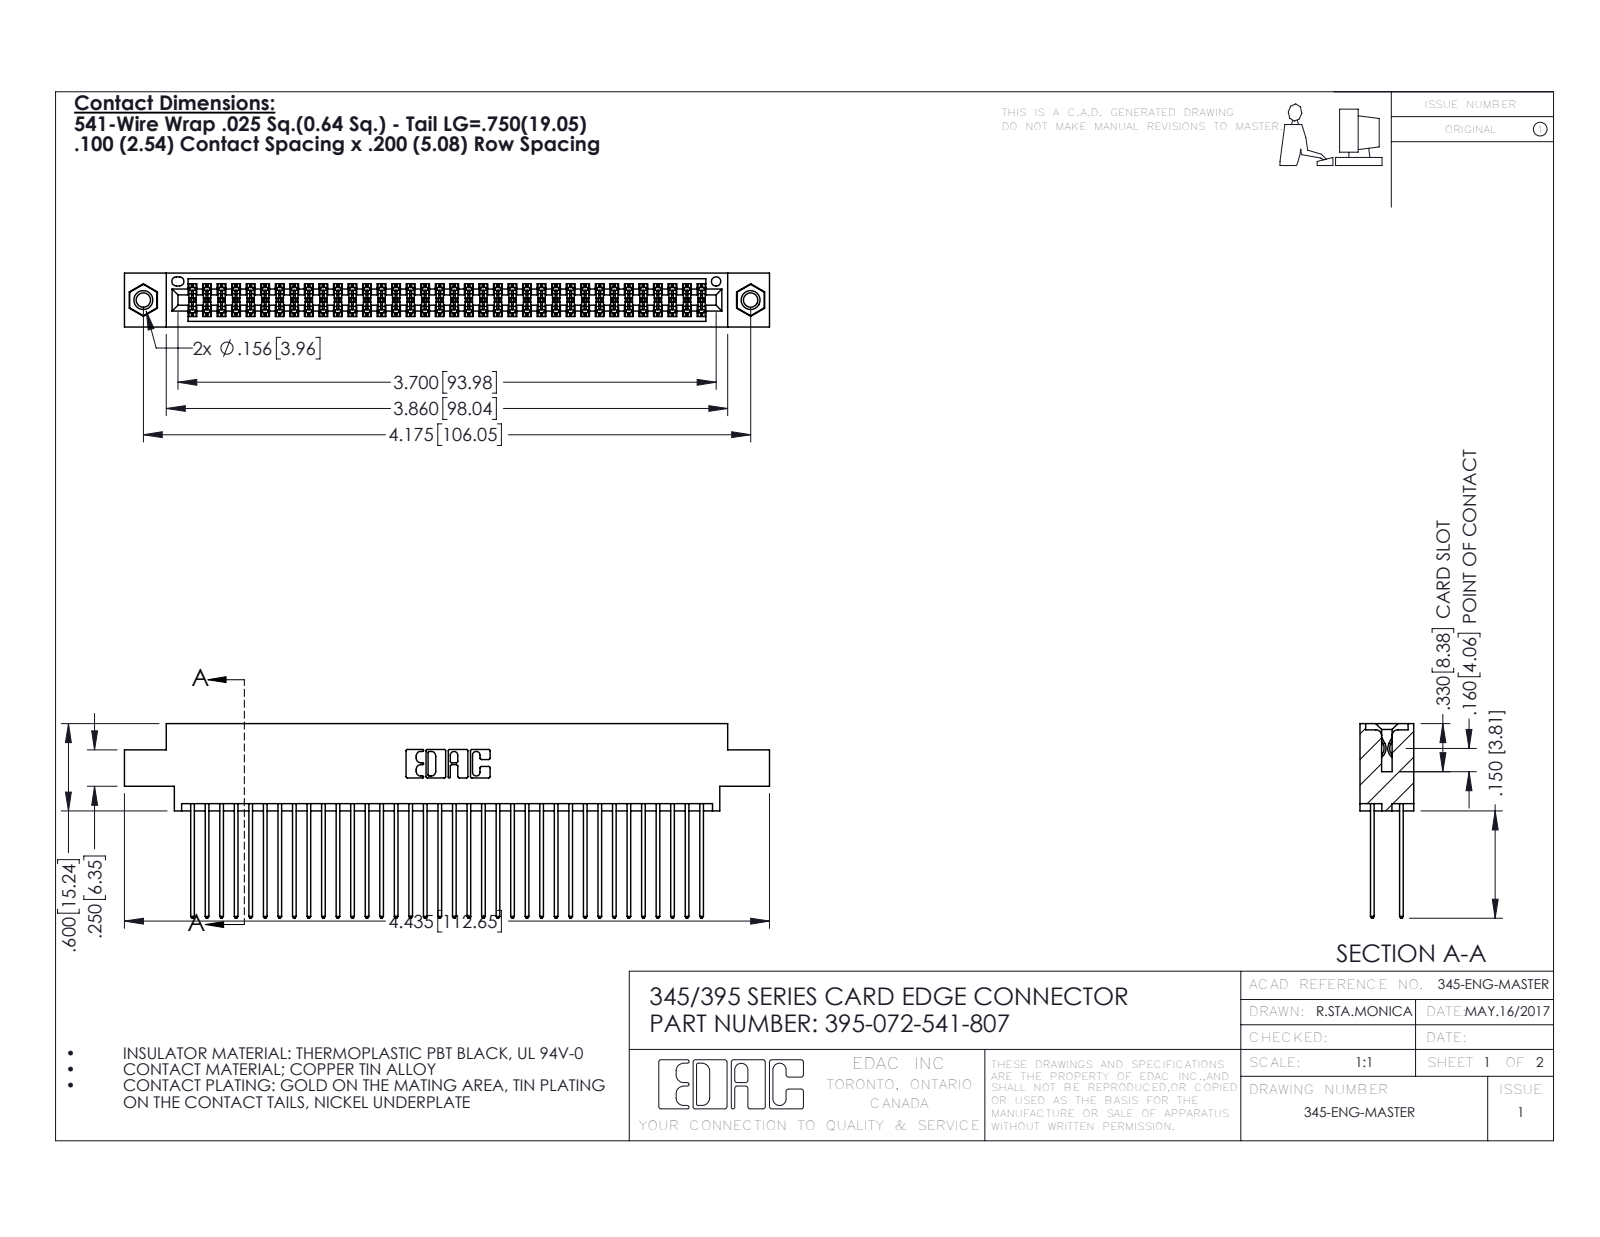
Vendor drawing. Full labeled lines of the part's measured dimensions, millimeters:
Part name (STEP PRODUCT): 345 Part_0.170 Offset - 0.156 Dia-TI; 345-250-001_345-250-005-103; 395-072-541-807; 345-292-001_345-293-141
STEP written by: SolidWorks 2016 (CONFIG_CONTROL_DESIGN)
Units: millimetres
Bodies: 75 solids, 3790 faces (2492 planar, 1282 cylindrical, 16 other)
Overall size (bounding box): 112.6 × 34 × 9.4
Volume: 11 200 mm³ · Surface area: 18 520 mm²
Round holes (diameter × count): ⌀2.5 ×2, ⌀3.2 ×2, ⌀4 ×2, ⌀1.6 ×1
Round bosses / shafts (diameter × count): ⌀3.9 ×2
Partial cylindrical surfaces — rounded edges, fillets, slot ends (radius × count): R0.2 ×108, R0.3 ×72, R0.3 ×22, R0.2 ×6, R0.8 ×6, R0.7 ×3, R0.4 ×2, R0.5 ×2
Main face-to-face distances: 1.8, 7.6, 5.1, 2.5, 6.9, 0.6, 9.4, 5.7, 4.4, 3.8
Hole centre spacings: 6.9, 100.1, 106
